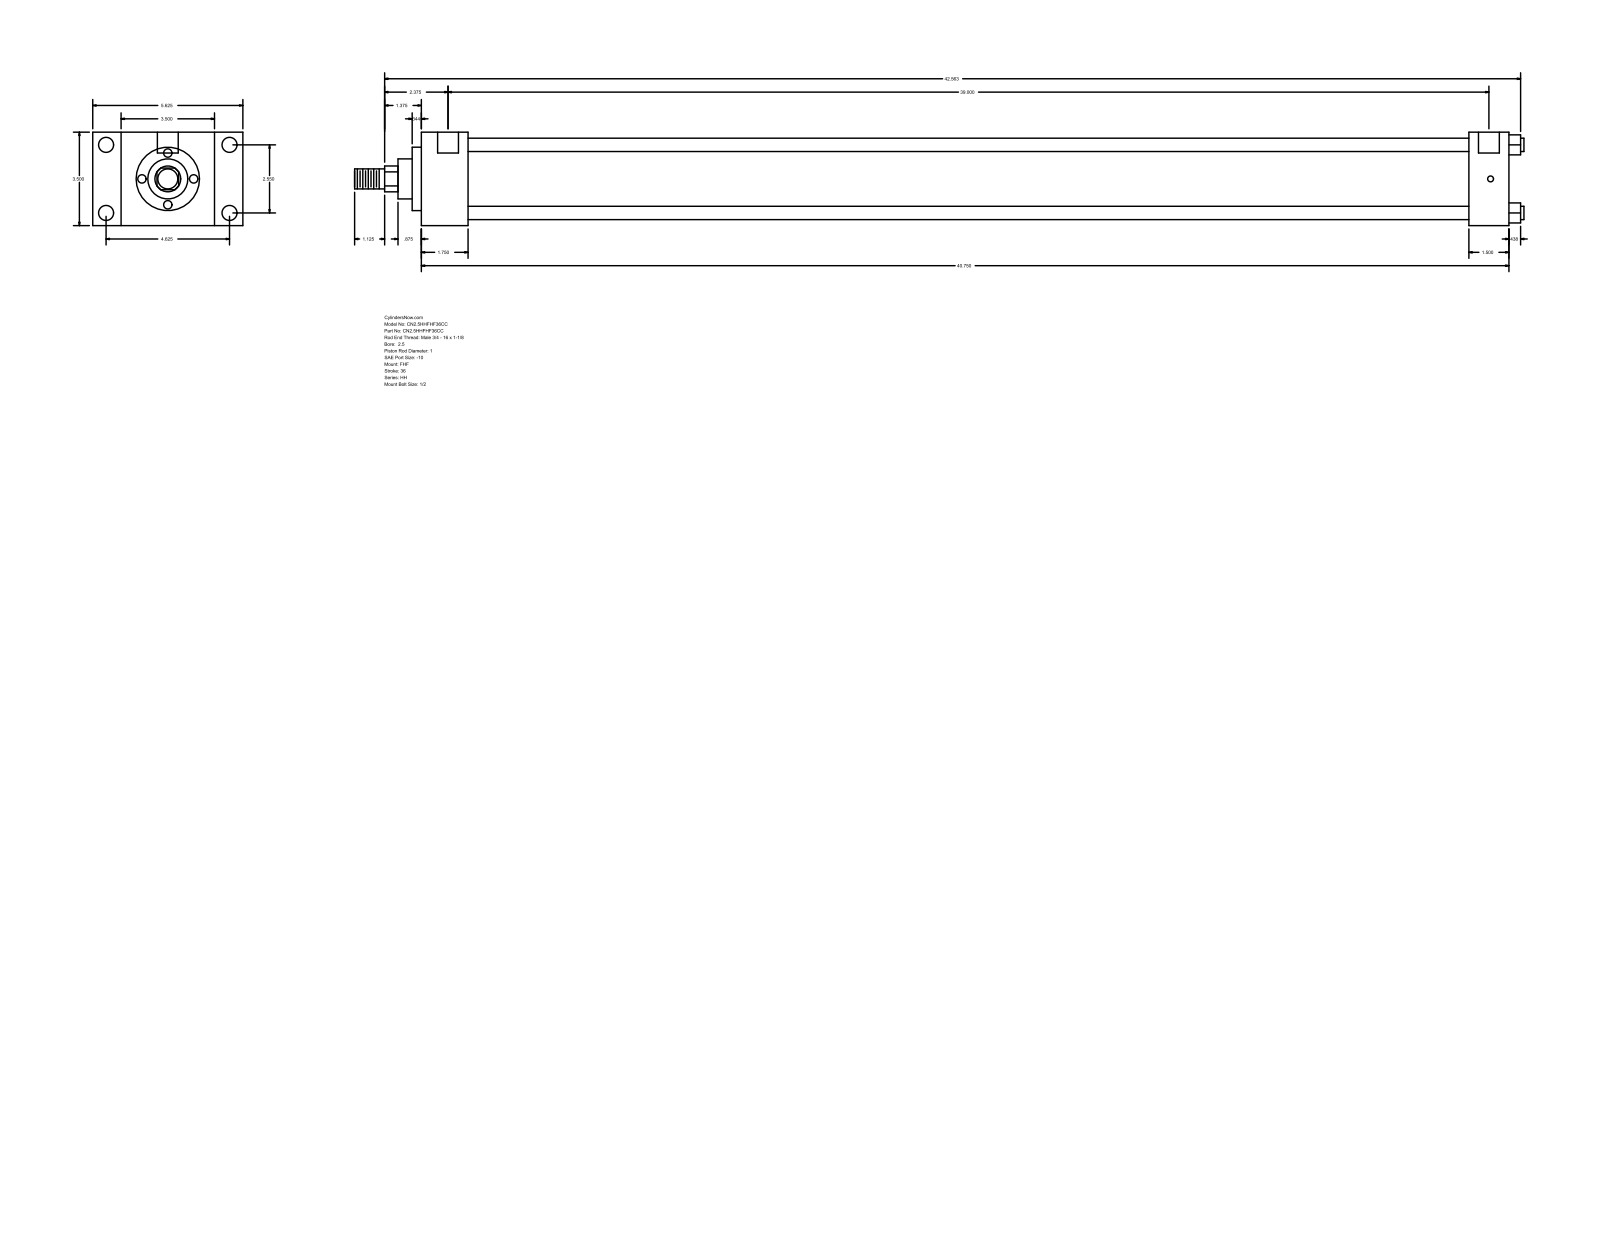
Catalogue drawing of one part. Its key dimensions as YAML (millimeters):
part_name: "HH_FHF__0250_1"
step_written_by: "GSSL Pune (CONFIG_CONTROL_DESIGN)"
units: millimeters
bodies: {solids: 0, faces: 90, planar: 61, cylindrical: 29, other: 0}
overall_size: [1112.84, 142.88, 88.9]
round_holes:
  - {diameter: 5.56, count: 4}
  - {diameter: 14.3, count: 4}
  - {diameter: 19.84, count: 2}
round_bosses_or_shafts:
  - {diameter: 12.7, count: 4}
  - {diameter: 73.03, count: 1}
  - {diameter: 60.33, count: 1}
  - {diameter: 38.1, count: 1}
  - {diameter: 25.4, count: 1}
  - {diameter: 19.05, count: 1}
partial_cylinders:
  - {radius: 12.29, count: 1}
face_to_face_distances: [88.9, 44.46, 26.99, 115.89, 1035.05, 990.59, 142.88, 996.96, 952.5, 38.09]
hole_center_spacings: [1.59, 64.76, 117.48, 134.15, 992.18, 993.77, 990.59]
